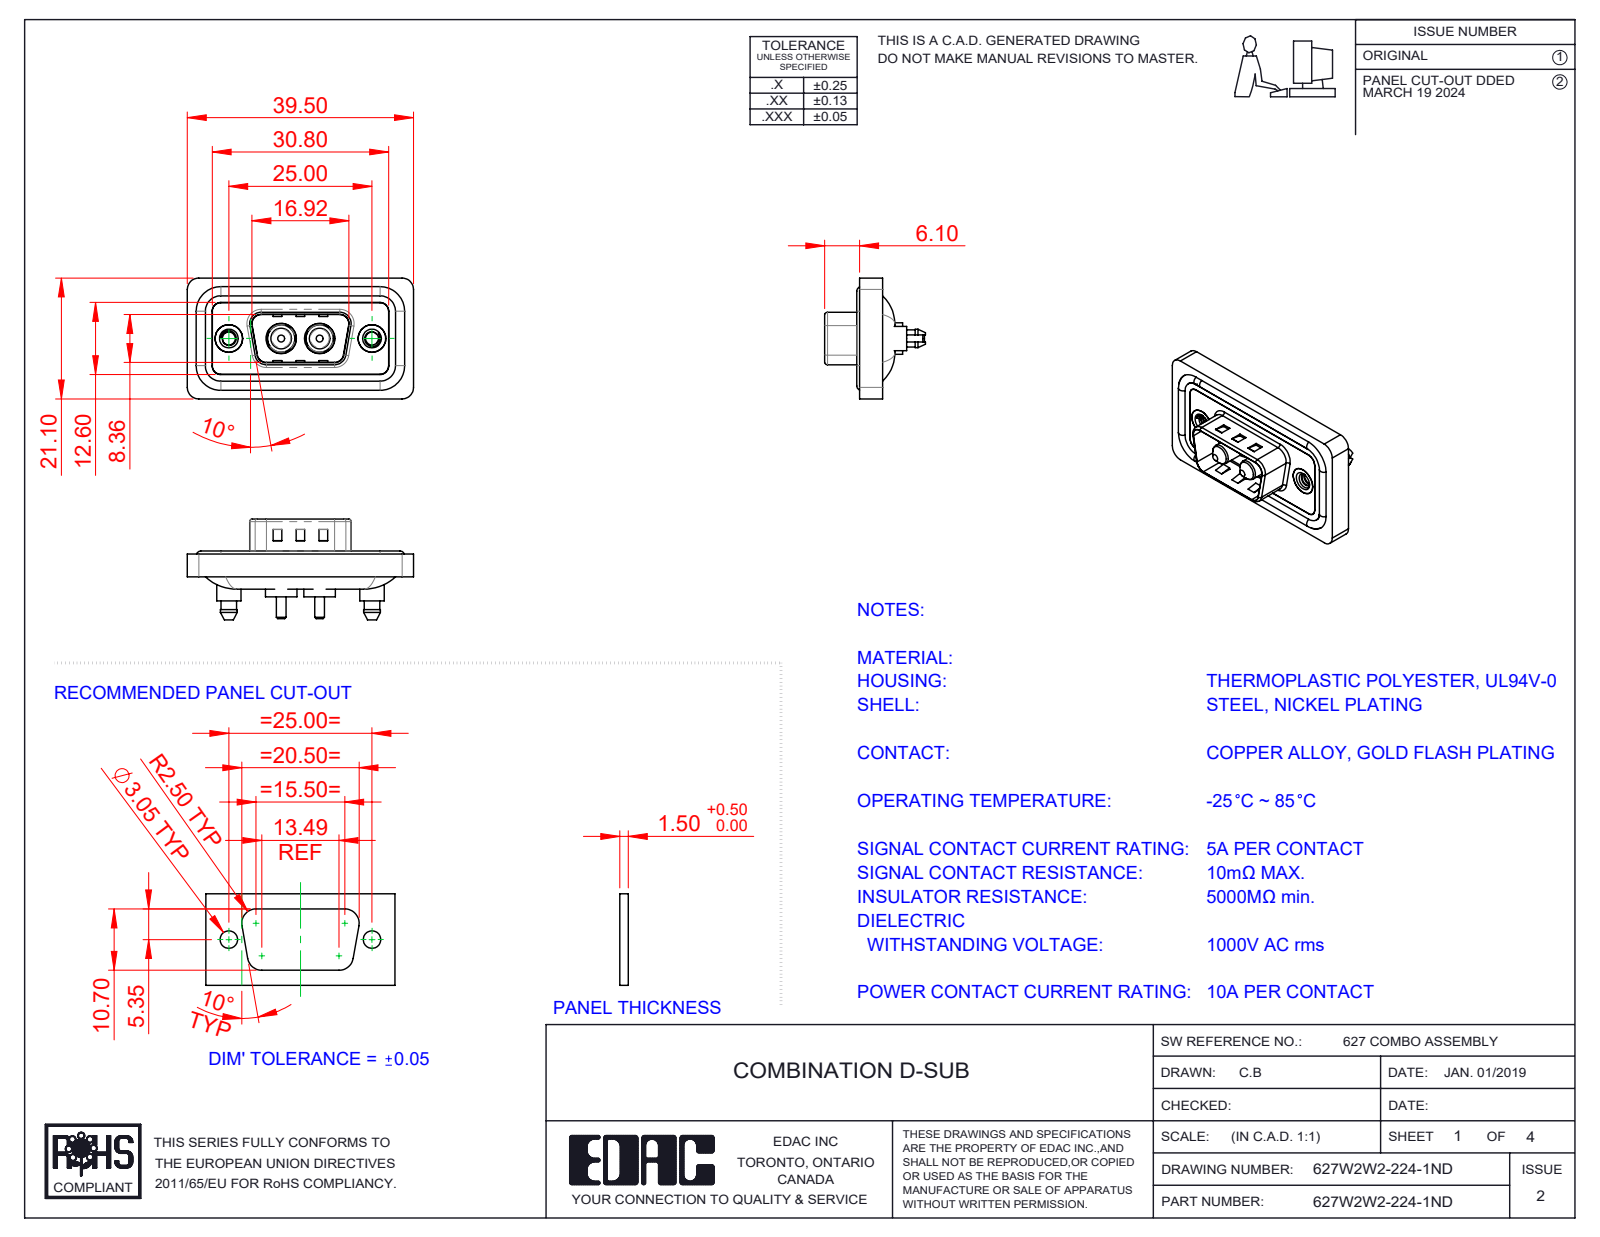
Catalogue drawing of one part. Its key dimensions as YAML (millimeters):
part_name: "627Combo Shell Front_09 Contacts; 627Combo Threaded Boardlock_5; 627Combo Waterproof Housing_09 Contacts; 627Combo Housing_2W2 (+4 more)"
step_written_by: "SolidWorks 2023 (CONFIG_CONTROL_DESIGN)"
units: millimeters
bodies: {solids: 11, faces: 547, planar: 181, cylindrical: 258, other: 108}
overall_size: [39.5, 21.1, 17.6]
volume: 4566
surface_area: 7295
round_holes:
  - {diameter: 2.26, count: 2}
  - {diameter: 4, count: 2}
  - {diameter: 4.8, count: 2}
  - {diameter: 4.85, count: 2}
  - {diameter: 5, count: 2}
  - {diameter: 5.3, count: 2}
round_bosses_or_shafts:
  - {diameter: 1.6, count: 4}
  - {diameter: 5.5, count: 2}
  - {diameter: 5.4, count: 2}
  - {diameter: 5.2, count: 2}
  - {diameter: 4.9, count: 2}
  - {diameter: 4.75, count: 2}
  - {diameter: 4.25, count: 2}
  - {diameter: 3.75, count: 2}
partial_cylinders:
  - {radius: 1.5, count: 24}
  - {radius: 2, count: 18}
  - {radius: 1.6, count: 10}
  - {radius: 0.5, count: 8}
  - {radius: 0.25, count: 4}
  - {radius: 0.6, count: 4}
  - {radius: 0.65, count: 4}
  - {radius: 0.9, count: 4}
face_to_face_distances: [0.4, 1.1, 2.9, 1.5, 3.1, 0.5, 1.6, 4, 0.7, 2.5]
hole_center_spacings: [9.14, 15.86, 6.72, 25]
